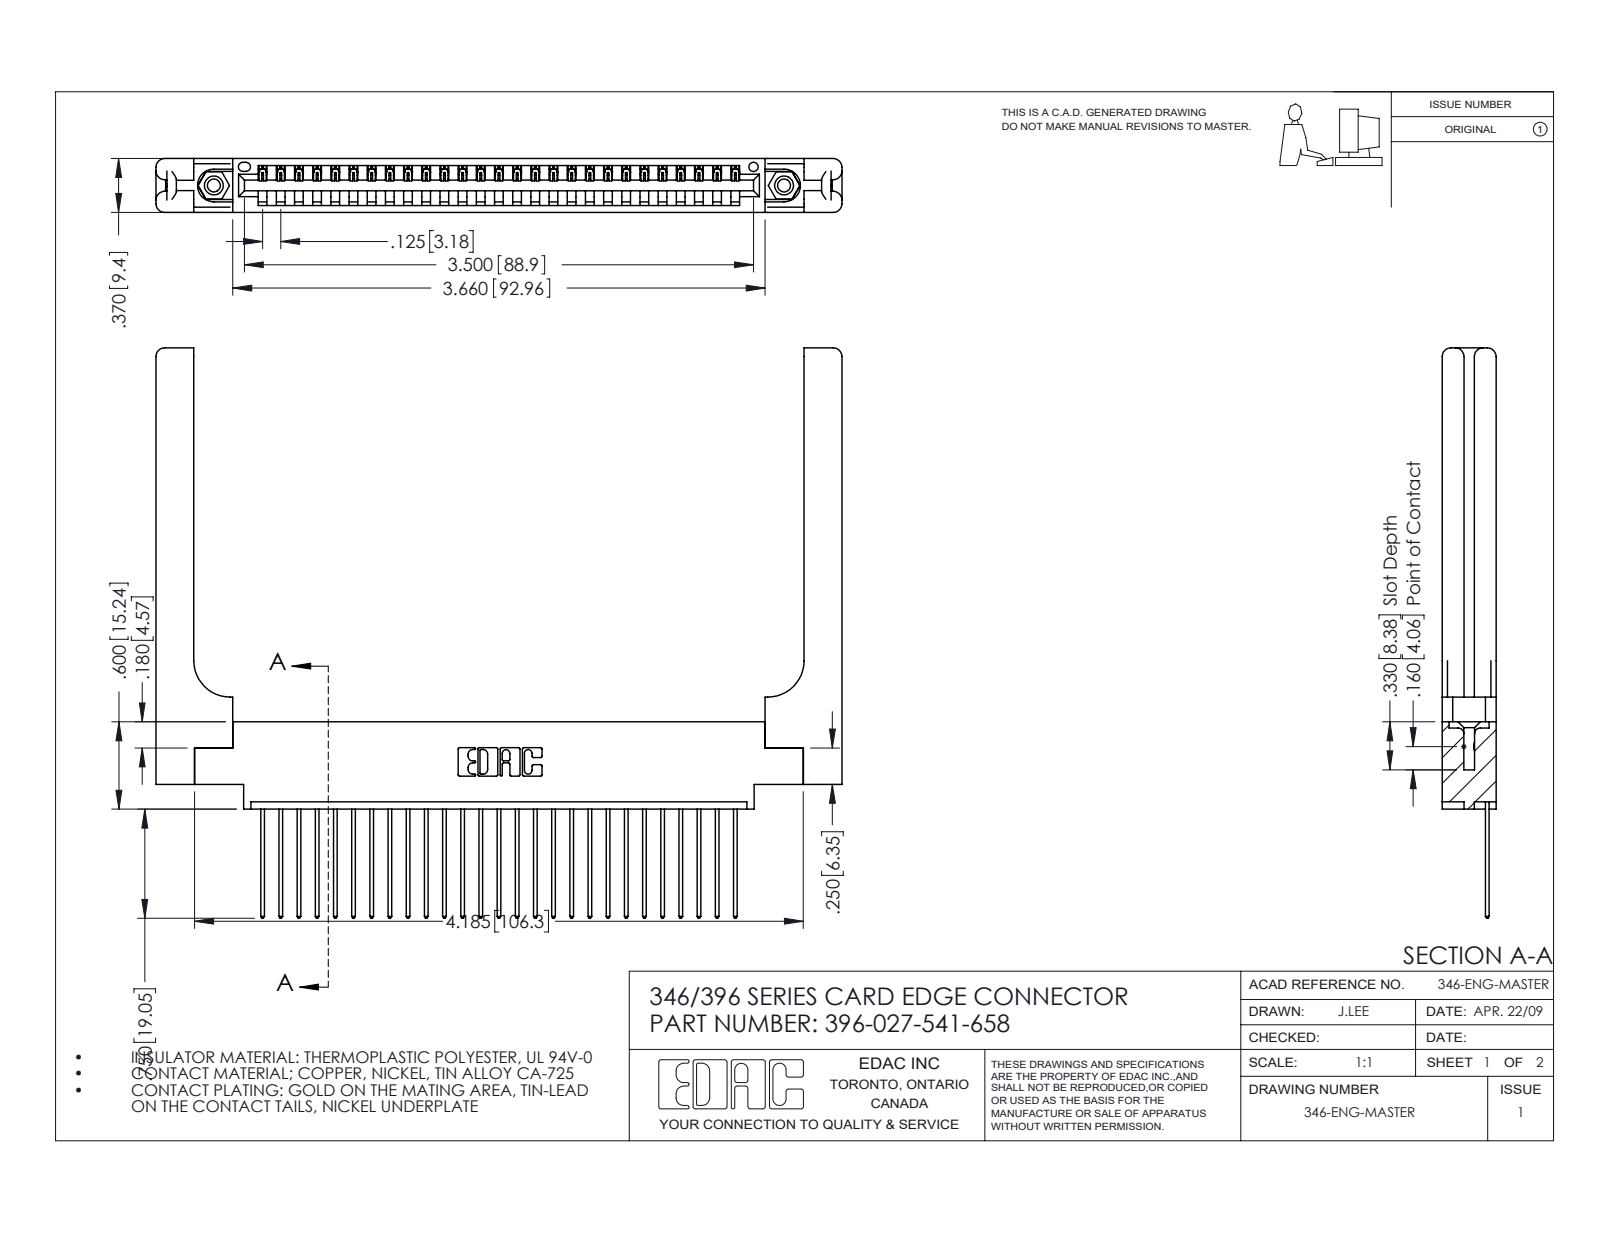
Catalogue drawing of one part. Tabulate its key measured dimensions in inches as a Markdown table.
| quantity | value |
| --- | --- |
| part name | 345-250-001_345-250-001-102; 346-220-058_345-220-058; 396-027-541-658; 346 Part_0.170 Offset - 0.156 Dia-TH (+1 more) |
| STEP written by | SolidWorks 2016 (CONFIG_CONTROL_DESIGN) |
| units | inches |
| bodies | 32 solids, 1948 faces (1308 planar, 580 cylindrical, 60 other) |
| overall size | 4.716 × 3.92 × 0.37 |
| volume | 1.148 in³ |
| surface area | 30.72 in² |
| round holes (diameter × count) | 0.089 × 2, 0.125 × 2, 0.156 × 2, 0.064 × 1 |
| round bosses / shafts (diameter × count) | 0.155 × 2 |
| partial cylindrical surfaces (radius × count) | 0.006 × 54, 0.01 × 54, 0.01 × 22, 0.06 × 16, 0.007 × 6, 0.031 × 6, 0.026 × 3, 0.03 × 2 |
| main face-to-face distances | 0.37, 0.072, 0.048, 0.322, 0.148, 0.15, 0.25, 0.298, 0.025, 0.076 |
| hole center spacings | 0.246, 3.712, 3.92 |
